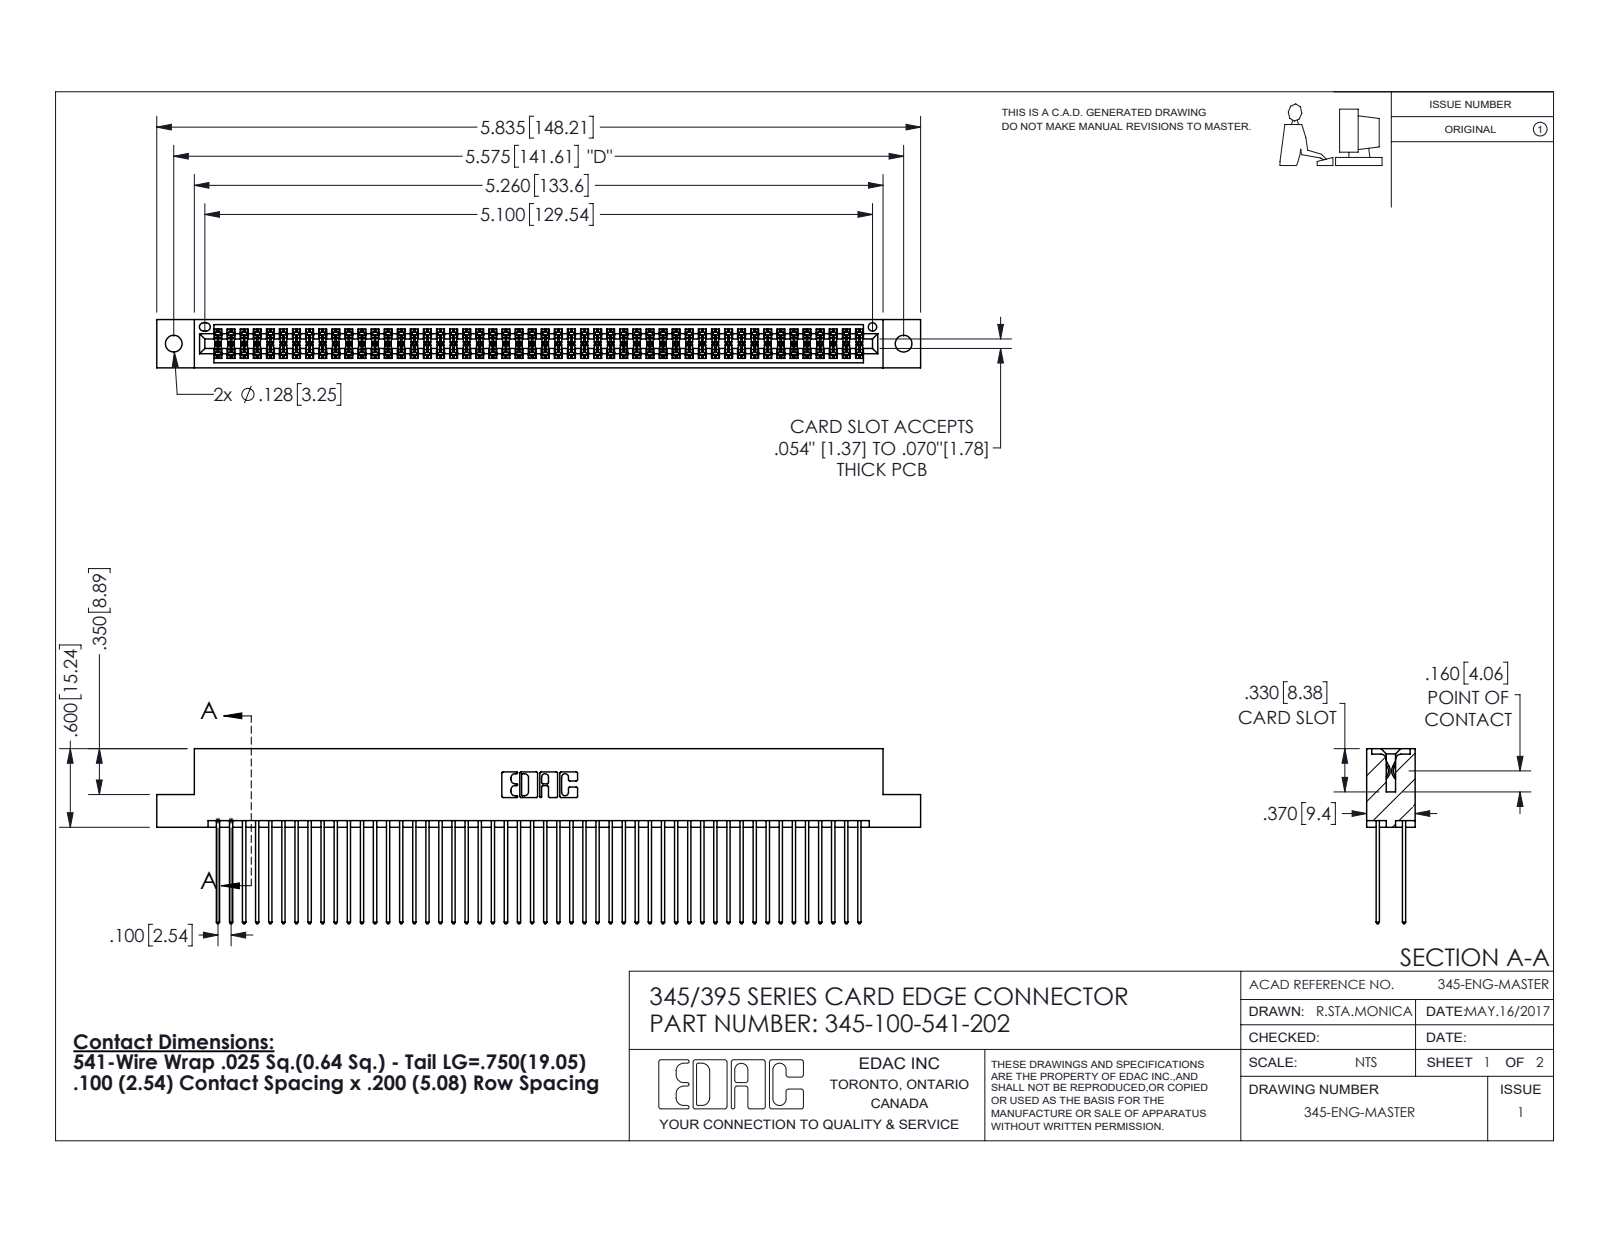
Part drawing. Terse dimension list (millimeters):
name: 345 Part_Flush Mounting Lugs - 0.128 Dia; 345-100-541-202; 345-292-001_345-293-141
written by: SolidWorks 2016 (CONFIG_CONTROL_DESIGN)
unit: mm
bodies: 101 solids, 5126 faces (3380 planar, 1746 cylindrical, 0 other)
size: 148.2 × 34 × 9.4
volume: 15 000 mm³; area: 24 760 mm²
holes: 2× ⌀3.3, 1× ⌀1.6
rounds: 150× R0.2, 100× R0.3, 22× R0.3, 6× R0.2, 6× R0.8, 3× R0.7, 2× R0.4, 2× R0.5
face distances: 7.6, 1.8, 5.1, 2.5, 6.9, 0.6, 5.7, 9.4, 4.4, 3.8
hole spacings: 6.9, 135.6, 141.6
